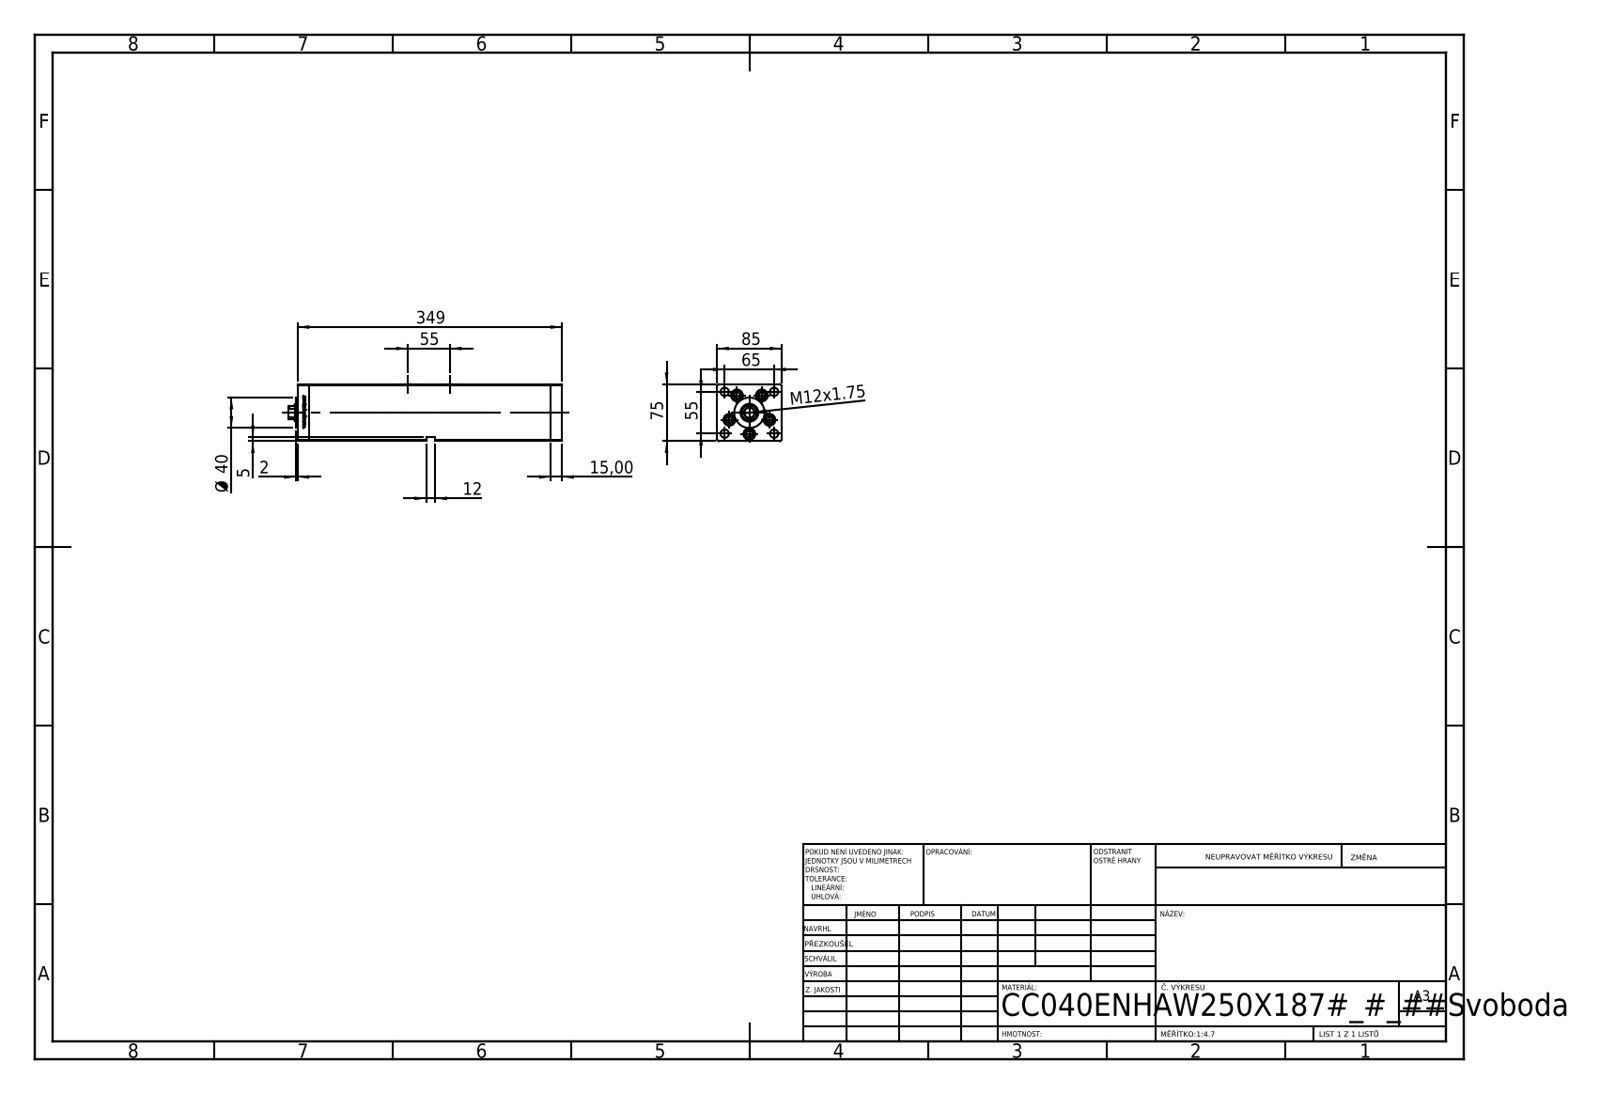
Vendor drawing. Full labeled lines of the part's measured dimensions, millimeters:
Part name (STEP PRODUCT): V220C_VC_E; V220C BACK_E; V220C_FRONT_E; ALLEN BOLT (+1 more)
STEP written by: SolidWorks 2019 (CONFIG_CONTROL_DESIGN)
Units: millimetres
Bodies: 14 solids, 1212 faces (473 planar, 165 cylindrical, 574 other)
Overall size (bounding box): 360 × 85 × 75
Volume: 1 871 000 mm³ · Surface area: 262 970 mm²
Round holes (diameter × count): ⌀11 ×9, ⌀15.5 ×5, ⌀10.5 ×4, ⌀16.5 ×4, ⌀2 ×2, ⌀13.16 ×2, ⌀13.5 ×1, ⌀22 ×1, ⌀23.5 ×1
Round bosses / shafts (diameter × count): ⌀14.5 ×5, ⌀8 ×5, ⌀40 ×1
Partial cylindrical surfaces — rounded edges, fillets, slot ends (radius × count): R0.93 ×2, R10.5 ×1
Main face-to-face distances: 85, 75, 15, 318.5, 333.5, 10.5, 64.5, 31.25, 53.75, 68.5
Hole centre spacings: 28, 42.57, 55, 65, 85.15, 16.86, 19.17, 32.33
